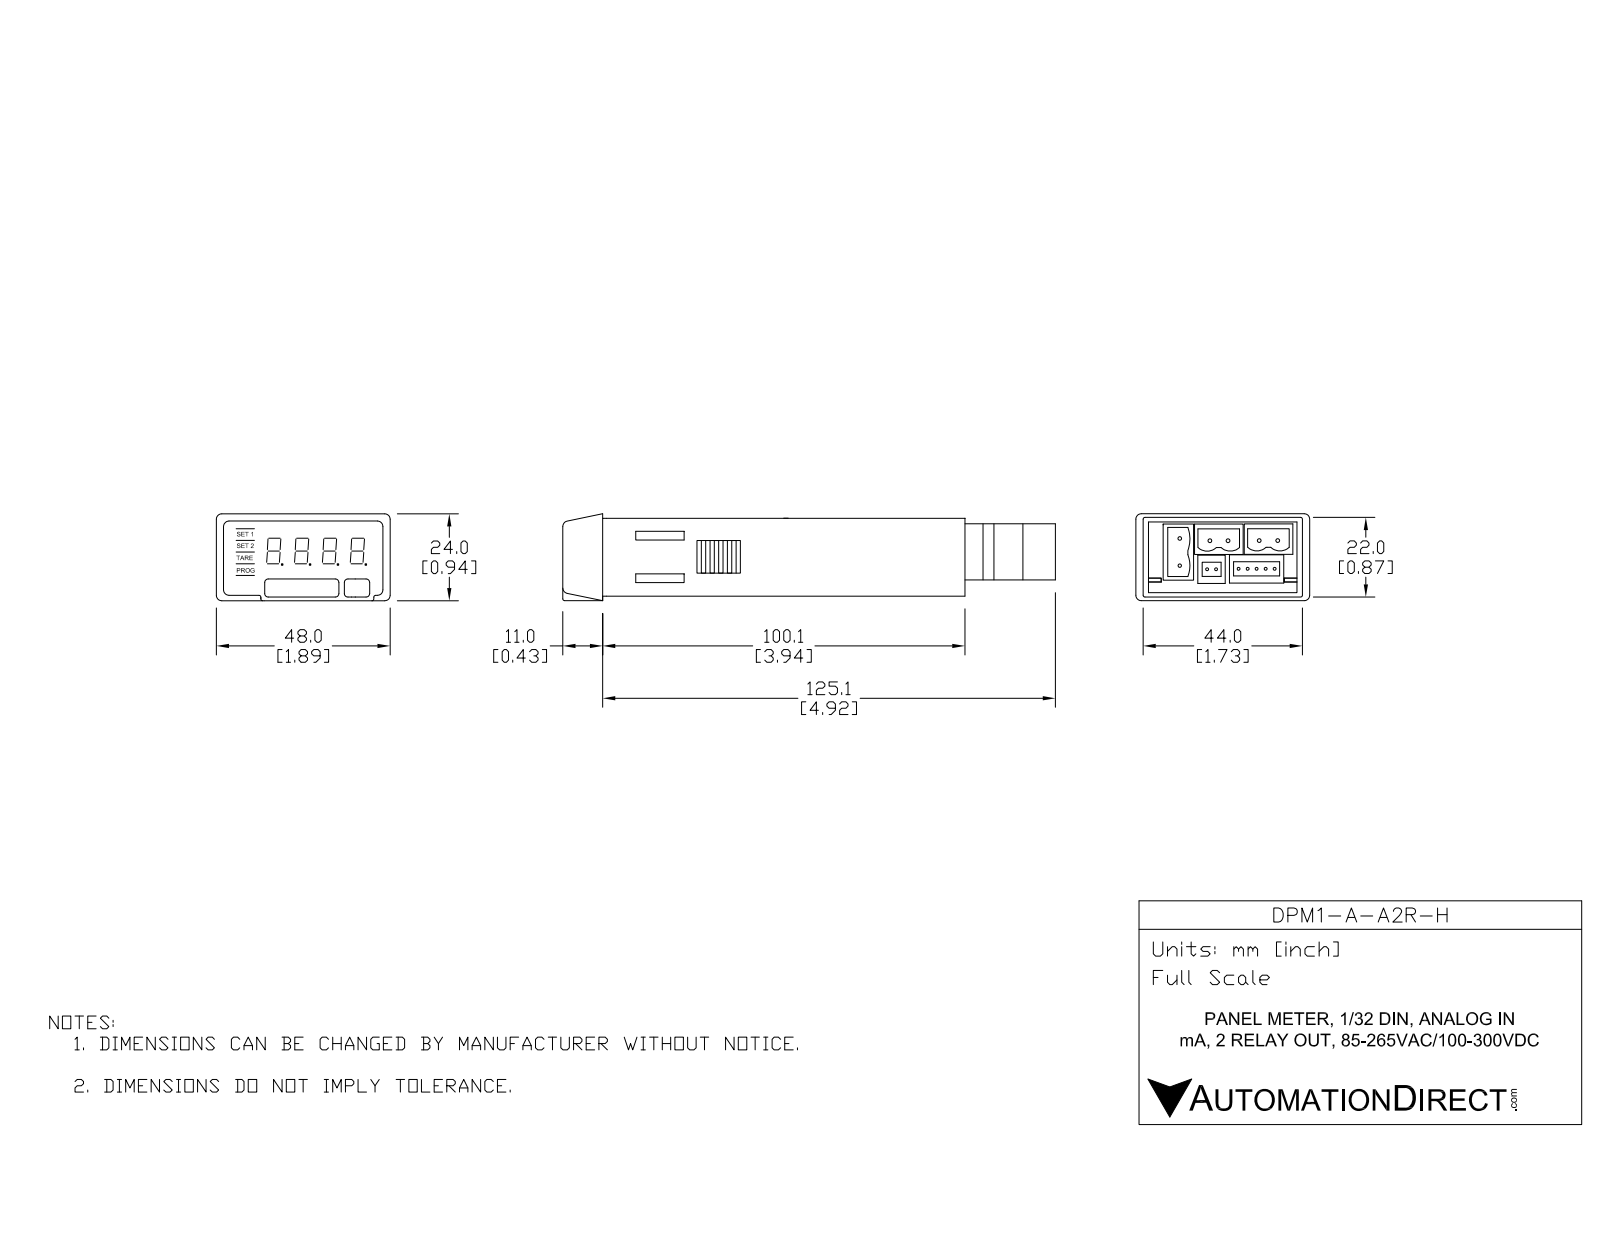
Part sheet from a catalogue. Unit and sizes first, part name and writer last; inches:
Units: inches
Overall size (bounding box): 5.354 × 1.89 × 0.98
Round holes (diameter × count): ⌀0.039 ×7, ⌀0.079 ×7, ⌀0.078 ×6, ⌀0.118 ×6, ⌀0.152 ×6
Partial cylindrical surfaces — rounded edges, fillets, slot ends (radius × count): R0.012 ×14, R0.014 ×14, R0.02 ×14, R0.07 ×7, R0.072 ×7, R0.121 ×6, R0.039 ×4, R0.025 ×2
Main face-to-face distances: 0.059, 0.807, 0.866, 0.748, 1.673, 1.732, 1.614, 0.051, 0.433, 4.315
Hole centre spacings: 0.54, 0.138, 0.197, 0.197, 0.201, 0.201, 0.276, 0.286
Volume: 2.573 in³ · Surface area: 60.7 in²
Bodies: 6 solids, 1467 faces (1124 planar, 167 cylindrical, 176 other)
Part name (STEP PRODUCT): DPM1-A-A2R-H
STEP written by: SolidWorks 2017 (AUTOMOTIVE_DESIGN)
